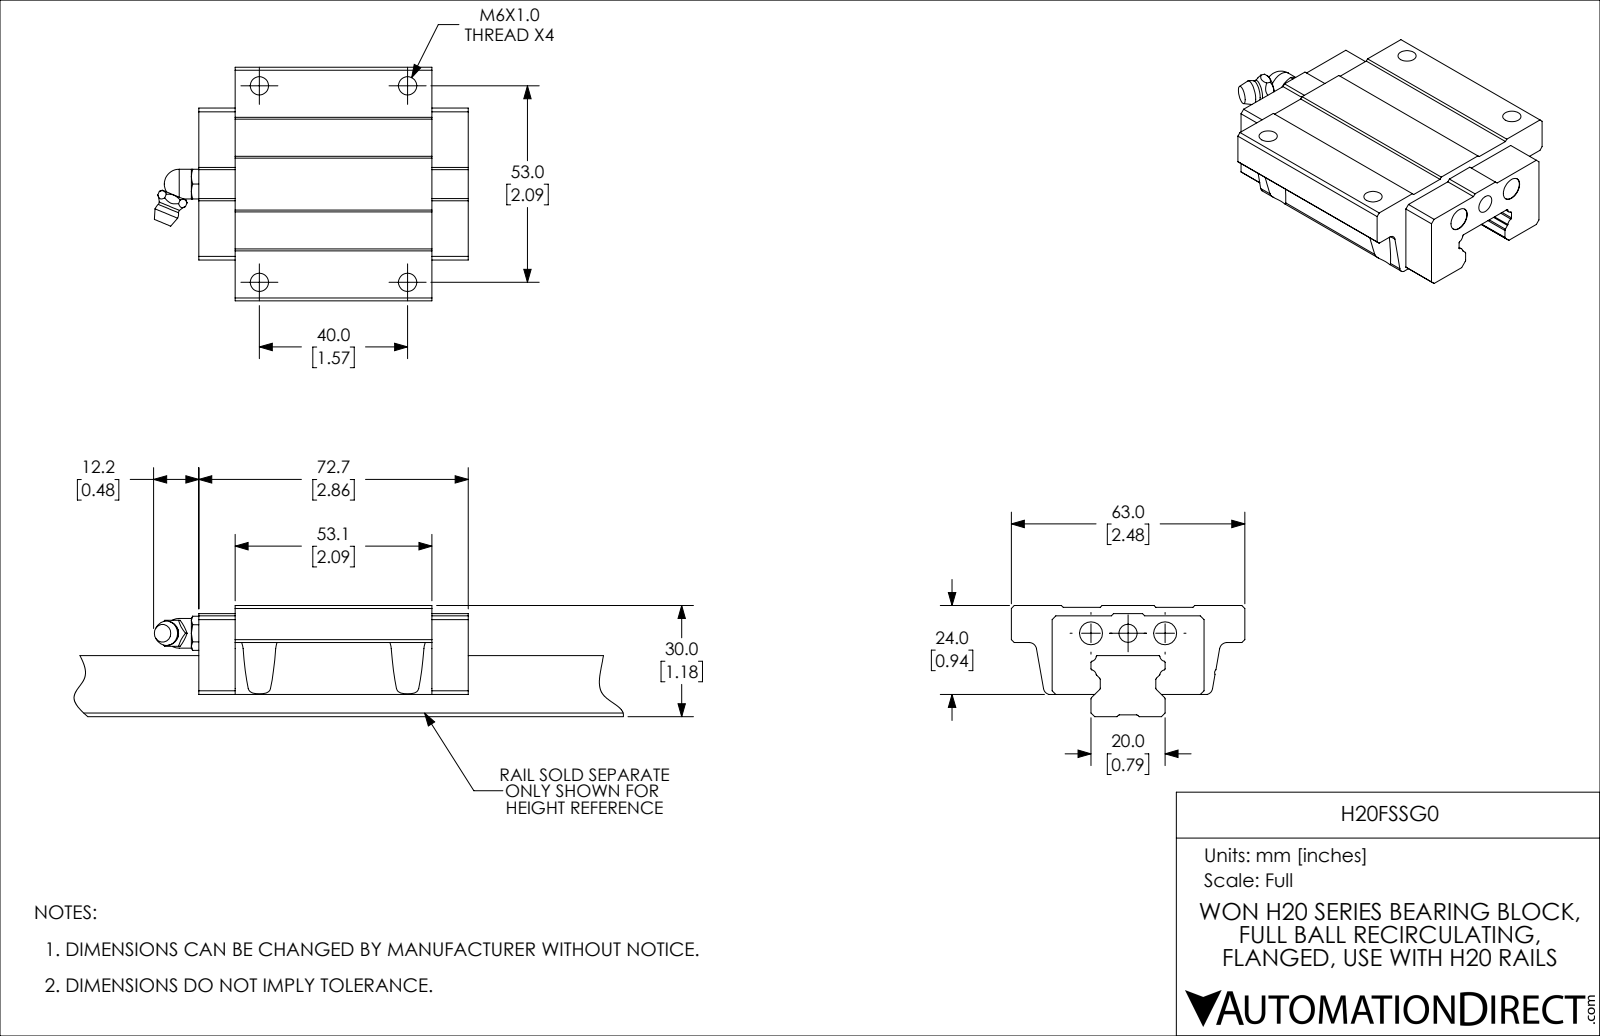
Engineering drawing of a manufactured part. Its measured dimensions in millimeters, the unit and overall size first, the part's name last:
Units: millimetres
Overall size (bounding box): 84.7 × 63 × 24
Round holes (diameter × count): ⌀4.92 ×5, ⌀6.2 ×2
Round bosses / shafts (diameter × count): ⌀8 ×1, ⌀6 ×1
Partial cylindrical surfaces — rounded edges, fillets, slot ends (radius × count): R0.5 ×8, R0.3 ×4, R1.6 ×4, R2 ×4, R4.75 ×4, R1 ×1
Main face-to-face distances: 24, 10.5, 13, 13.5, 23.5, 0.5, 9.8, 62.9, 11, 52
Hole centre spacings: 10, 40, 53, 66.4, 20
Volume: 71 296 mm³ · Surface area: 16 647 mm²
Bodies: 2 solids, 170 faces (85 planar, 63 cylindrical, 22 other)
Part name (STEP PRODUCT): H20FSSG0
STEP written by: SolidWorks 2019 (CONFIG_CONTROL_DESIGN)
